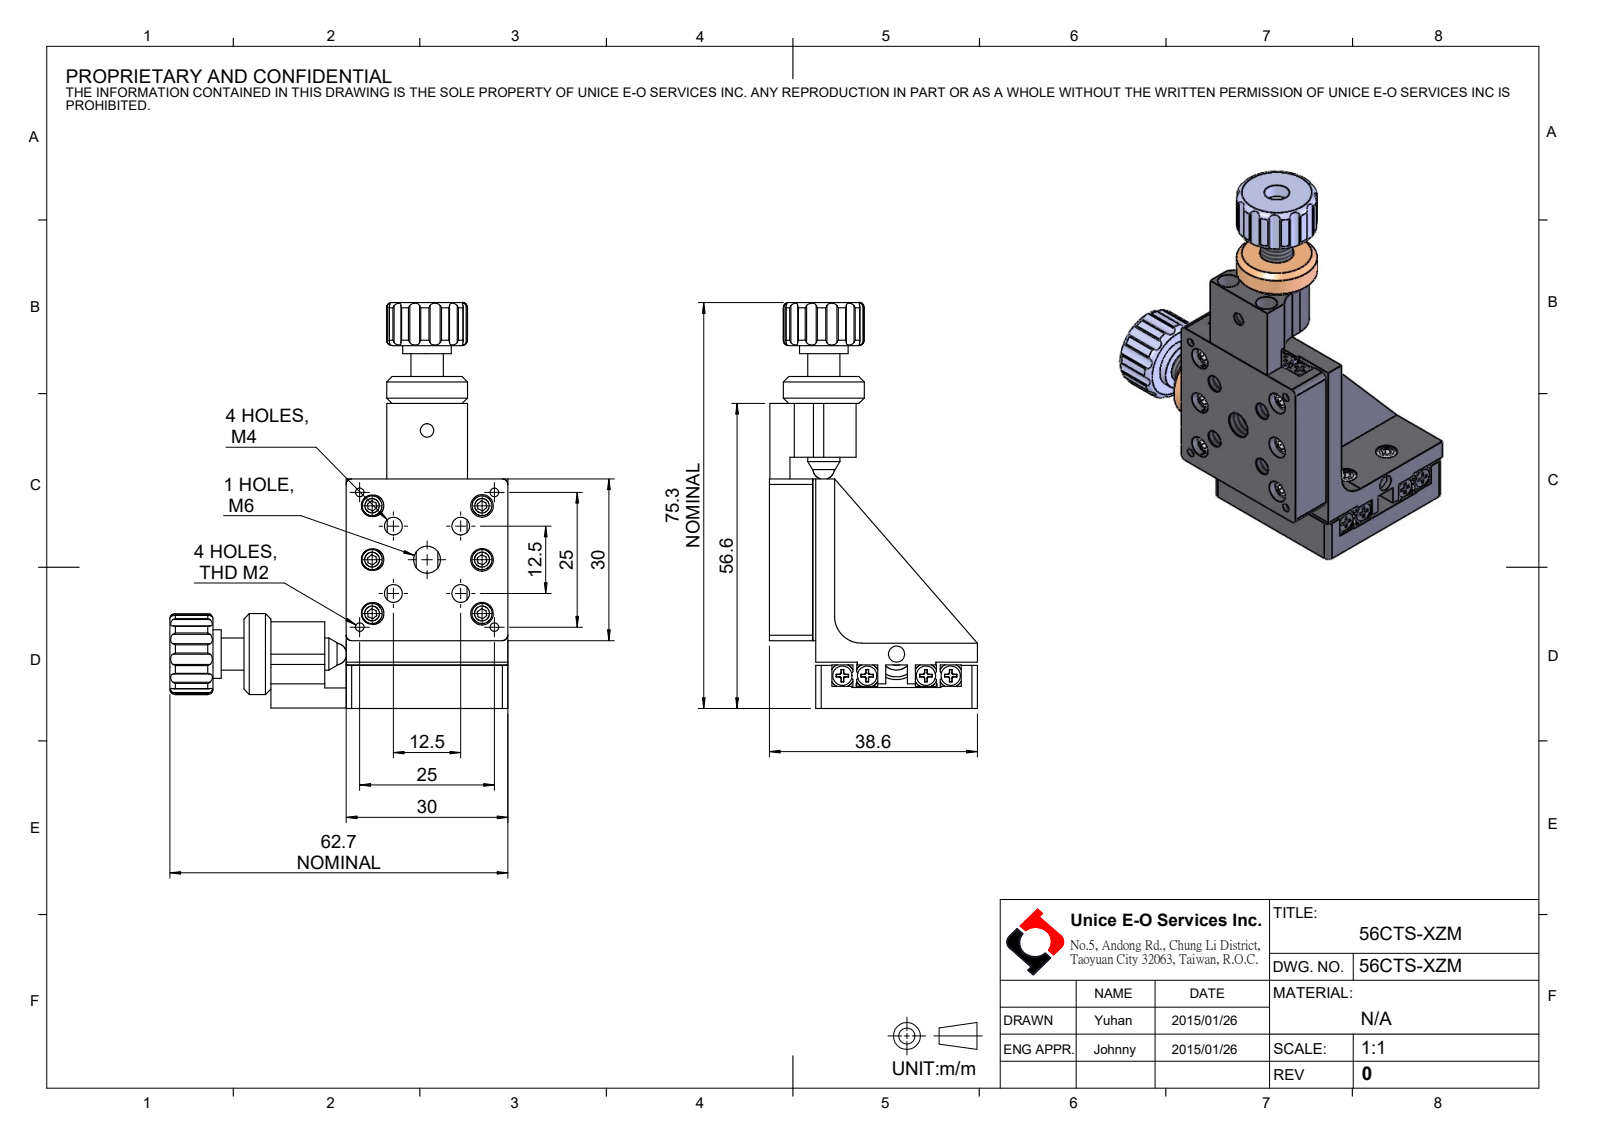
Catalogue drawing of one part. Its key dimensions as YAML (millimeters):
part_name: "56CTS-XZM"
step_written_by: "SolidWorks 2016 (CONFIG_CONTROL_DESIGN)"
units: millimeters
bodies: {solids: 73, faces: 1850, planar: 874, cylindrical: 626, other: 350}
overall_size: [75.33, 62.73, 38.6]
volume: 29383
surface_area: 29862
round_holes:
  - {diameter: 1.6, count: 48}
  - {diameter: 4, count: 18}
  - {diameter: 2.2, count: 12}
  - {diameter: 2.5, count: 8}
  - {diameter: 3.3, count: 8}
  - {diameter: 2.6, count: 6}
  - {diameter: 4.2, count: 6}
  - {diameter: 2.1, count: 4}
  - {diameter: 3, count: 2}
  - {diameter: 4.7, count: 2}
  - {diameter: 5, count: 2}
  - {diameter: 5.9, count: 2}
round_bosses_or_shafts:
  - {diameter: 3.7, count: 26}
  - {diameter: 2, count: 26}
  - {diameter: 3.6, count: 8}
  - {diameter: 1.95, count: 8}
  - {diameter: 3, count: 6}
  - {diameter: 15, count: 2}
  - {diameter: 9, count: 2}
partial_cylinders:
  - {radius: 0.3, count: 48}
  - {radius: 1.5, count: 24}
  - {radius: 1.25, count: 12}
  - {radius: 2, count: 12}
  - {radius: 1, count: 8}
  - {radius: 5, count: 5}
  - {radius: 6, count: 2}
face_to_face_distances: [4, 8, 0.5, 4.1, 3.9, 8.1, 4.5, 3.5, 8.5, 12]
hole_center_spacings: [15.5, 10, 8.84, 11.14, 18.45, 19.76, 4.9, 17.68]
